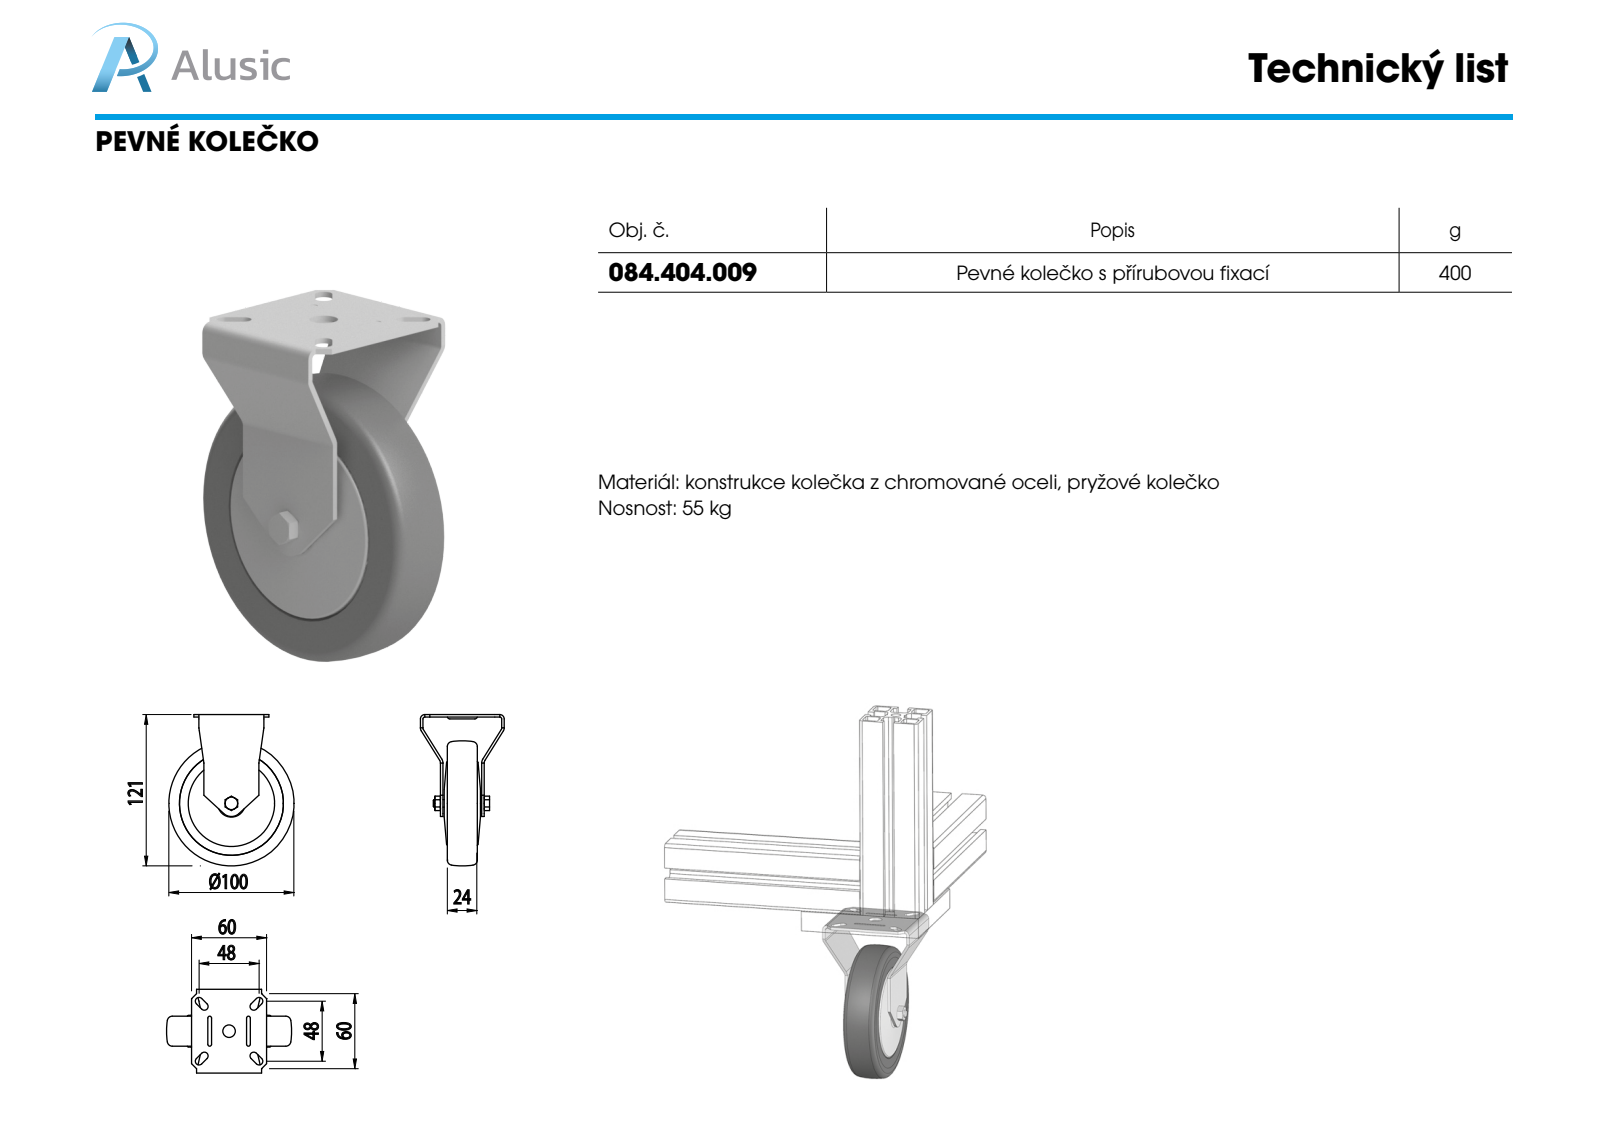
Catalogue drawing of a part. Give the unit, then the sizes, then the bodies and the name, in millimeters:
Units: millimetres
Overall size (bounding box): 121 × 100 × 67
Round holes (diameter × count): ⌀10 ×1, ⌀69 ×1, ⌀83.04 ×1
Round bosses / shafts (diameter × count): ⌀83 ×1, ⌀67 ×1, ⌀6 ×1
Partial cylindrical surfaces — rounded edges, fillets, slot ends (radius × count): R3 ×8, R1.5 ×6, R4 ×4, R2 ×2, R3.5 ×2, R6 ×2, R9 ×1
Main face-to-face distances: 2, 5.5, 29.5, 24, 35, 17, 48, 16, 21.5, 45.5
Bodies: 0 solids, 159 faces (73 planar, 52 cylindrical, 34 other)
Part name (STEP PRODUCT): 084.404.009
STEP written by: SolidWorks 2011 (CONFIG_CONTROL_DESIGN)
